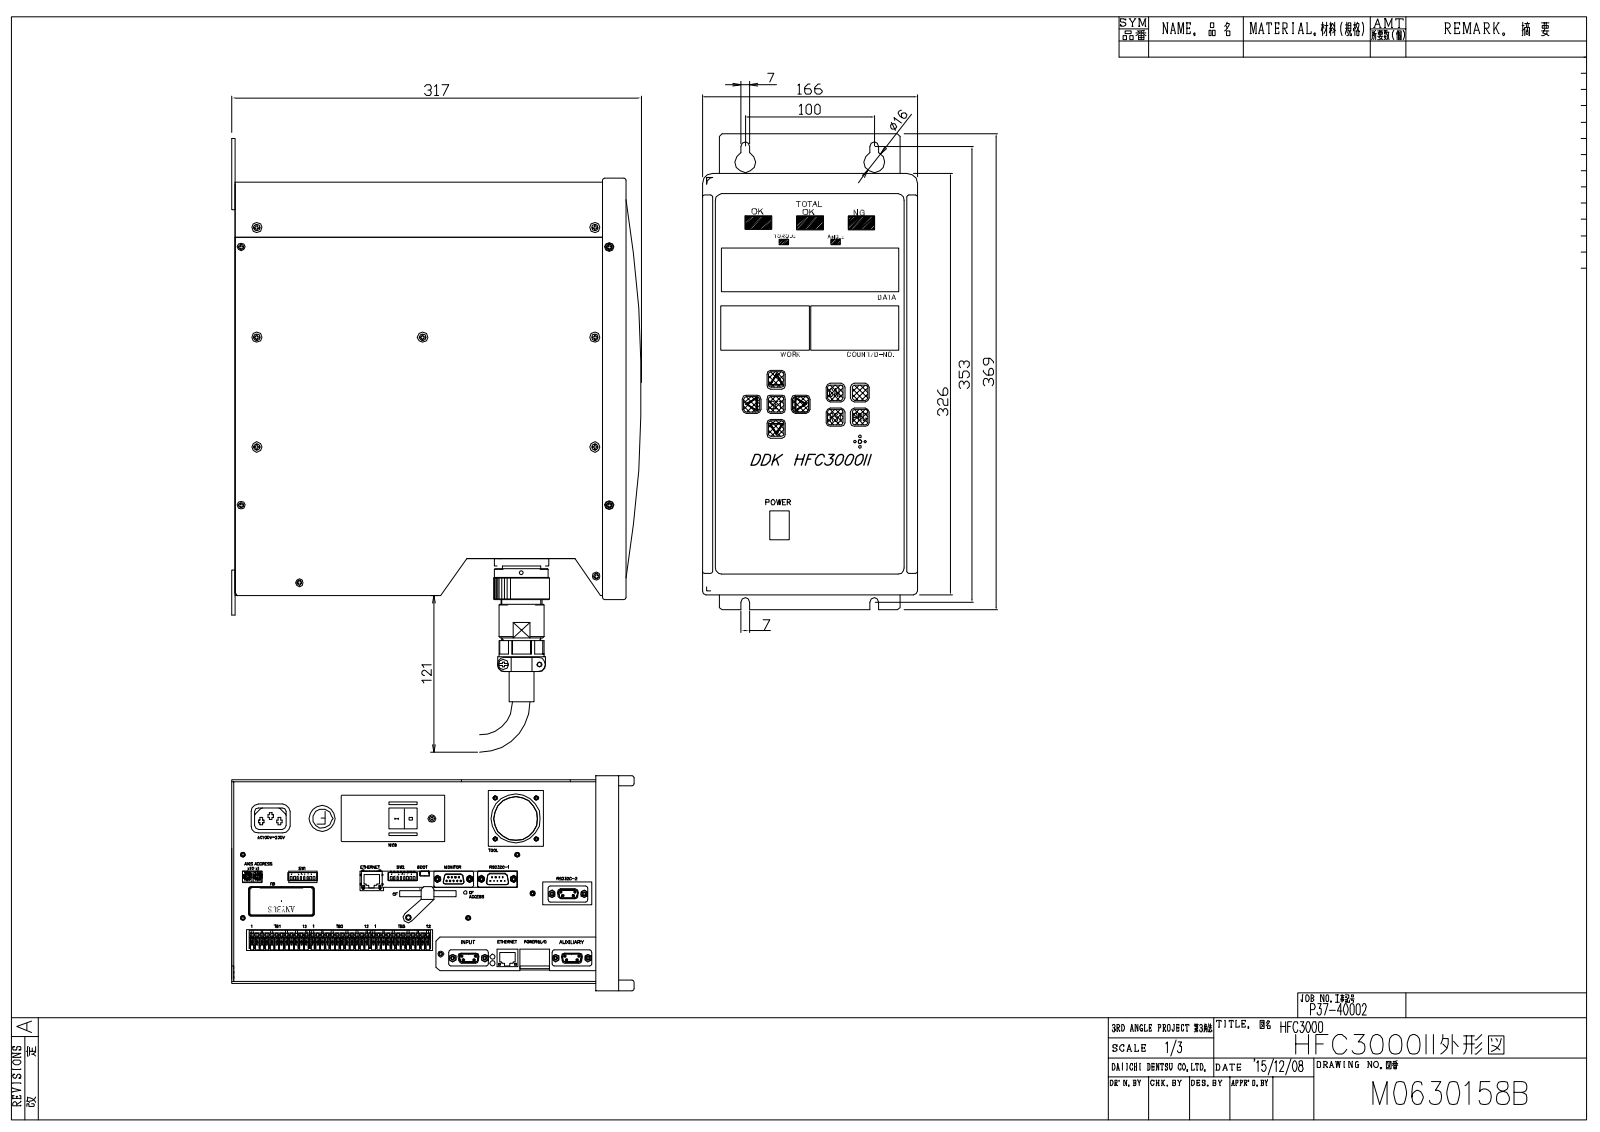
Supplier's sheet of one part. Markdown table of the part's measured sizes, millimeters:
| quantity | value |
| --- | --- |
| part name | HFC3000-2_コントローラー_Shrinkwrap_1 |
| STEP written by | Autodesk Inventor 2019 (AUTOMOTIVE_DESIGN) |
| units | millimeters |
| bodies | 351 solids, 11255 faces (8076 planar, 1571 cylindrical, 1608 other) |
| overall size | 368.8 × 317.3 × 168.93 |
| volume | 15 580 000 mm³ |
| surface area | 2 324 000 mm² |
| round holes (diameter × count) | 2.46 × 63, 3.2 × 47, 3.1 × 36, 7 × 27, 5 × 22, 4 × 21, 3.5 × 20, 3.24 × 17, 4.5 × 12, 2.38 × 10, 2.85 × 10, 3 × 10 |
| round bosses / shafts (diameter × count) | 3 × 57, 6 × 51, 5.9 × 36, 2.69 × 36, 5 × 18, 5.5 × 14, 4 × 13, 6.9 × 12 |
| partial cylindrical surfaces (radius × count) | 0.5 × 73, 1 × 63, 2 × 63, 0.2 × 58, 3 × 54, 0.15 × 37, 1.5 × 26, 0.1 × 18 |
| main face-to-face distances | 1.6, 1.2, 2.8, 158.8, 157.2, 156, 298.4, 17, 139, 157.6 |
| hole center spacings | 18, 36, 54, 100, 213.47, 216.32, 220.6, 20.79 |
